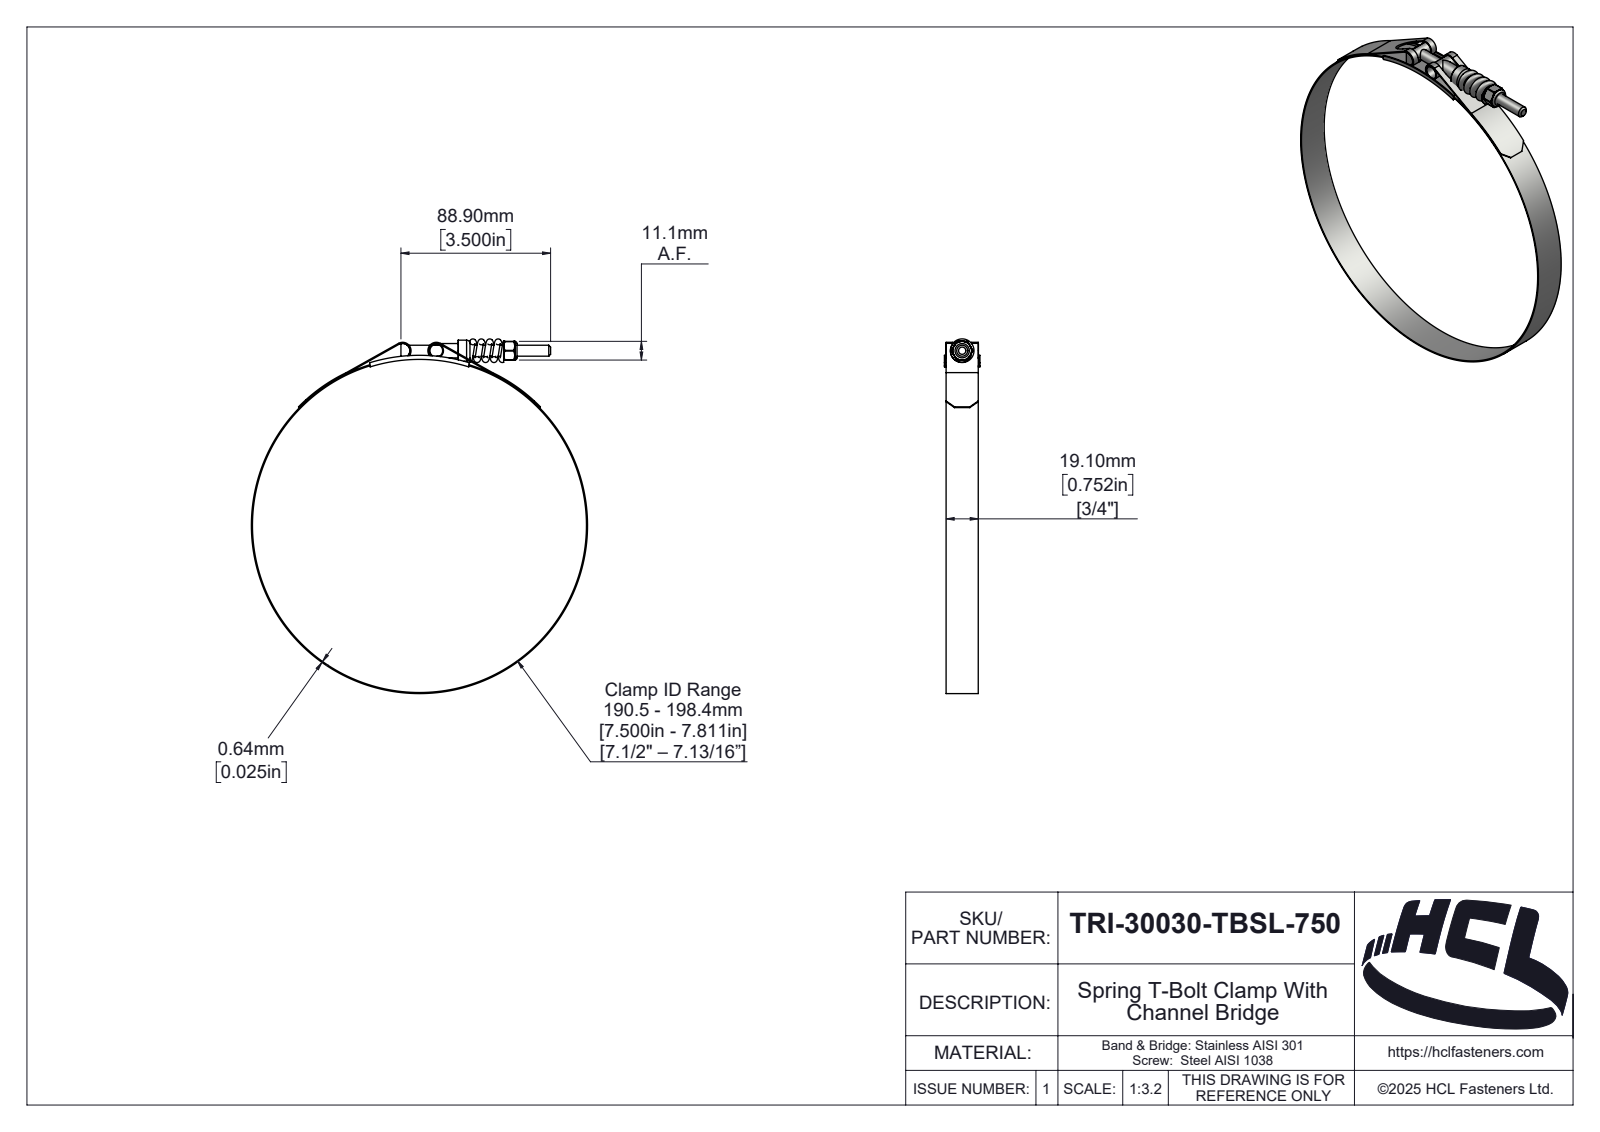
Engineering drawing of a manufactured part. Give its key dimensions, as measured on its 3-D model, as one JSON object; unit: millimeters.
{"part_name": "TRI-30030-TBSL-750", "step_written_by": "SolidWorks 2025 (AUTOMOTIVE_DESIGN)", "units": "millimeters", "bodies": {"solids": 7, "faces": 332, "planar": 48, "cylindrical": 122, "other": 162}, "overall_size": [210.58, 199.68, 21.1], "volume_mm3": 16493, "surface_area_mm2": 39225, "round_holes": [[5.4, 1], [6.35, 1], [6.5, 1], [7.52, 1], [198.4, 1]], "round_bosses_or_shafts": [[8.52, 2], [199.68, 1], [12.52, 1]], "partial_cylinders_radius": [[0.39, 6], [0.5, 2], [4.36, 2], [5, 2], [0.59, 1], [2.42, 1], [3.03, 1], [3.19, 1]], "face_to_face_distances": [0.64, 19.1, 1, 20.1, 20.46, 0.36, 19.46, 21.1, 61, 19.82], "hole_center_spacings": [104.2]}
